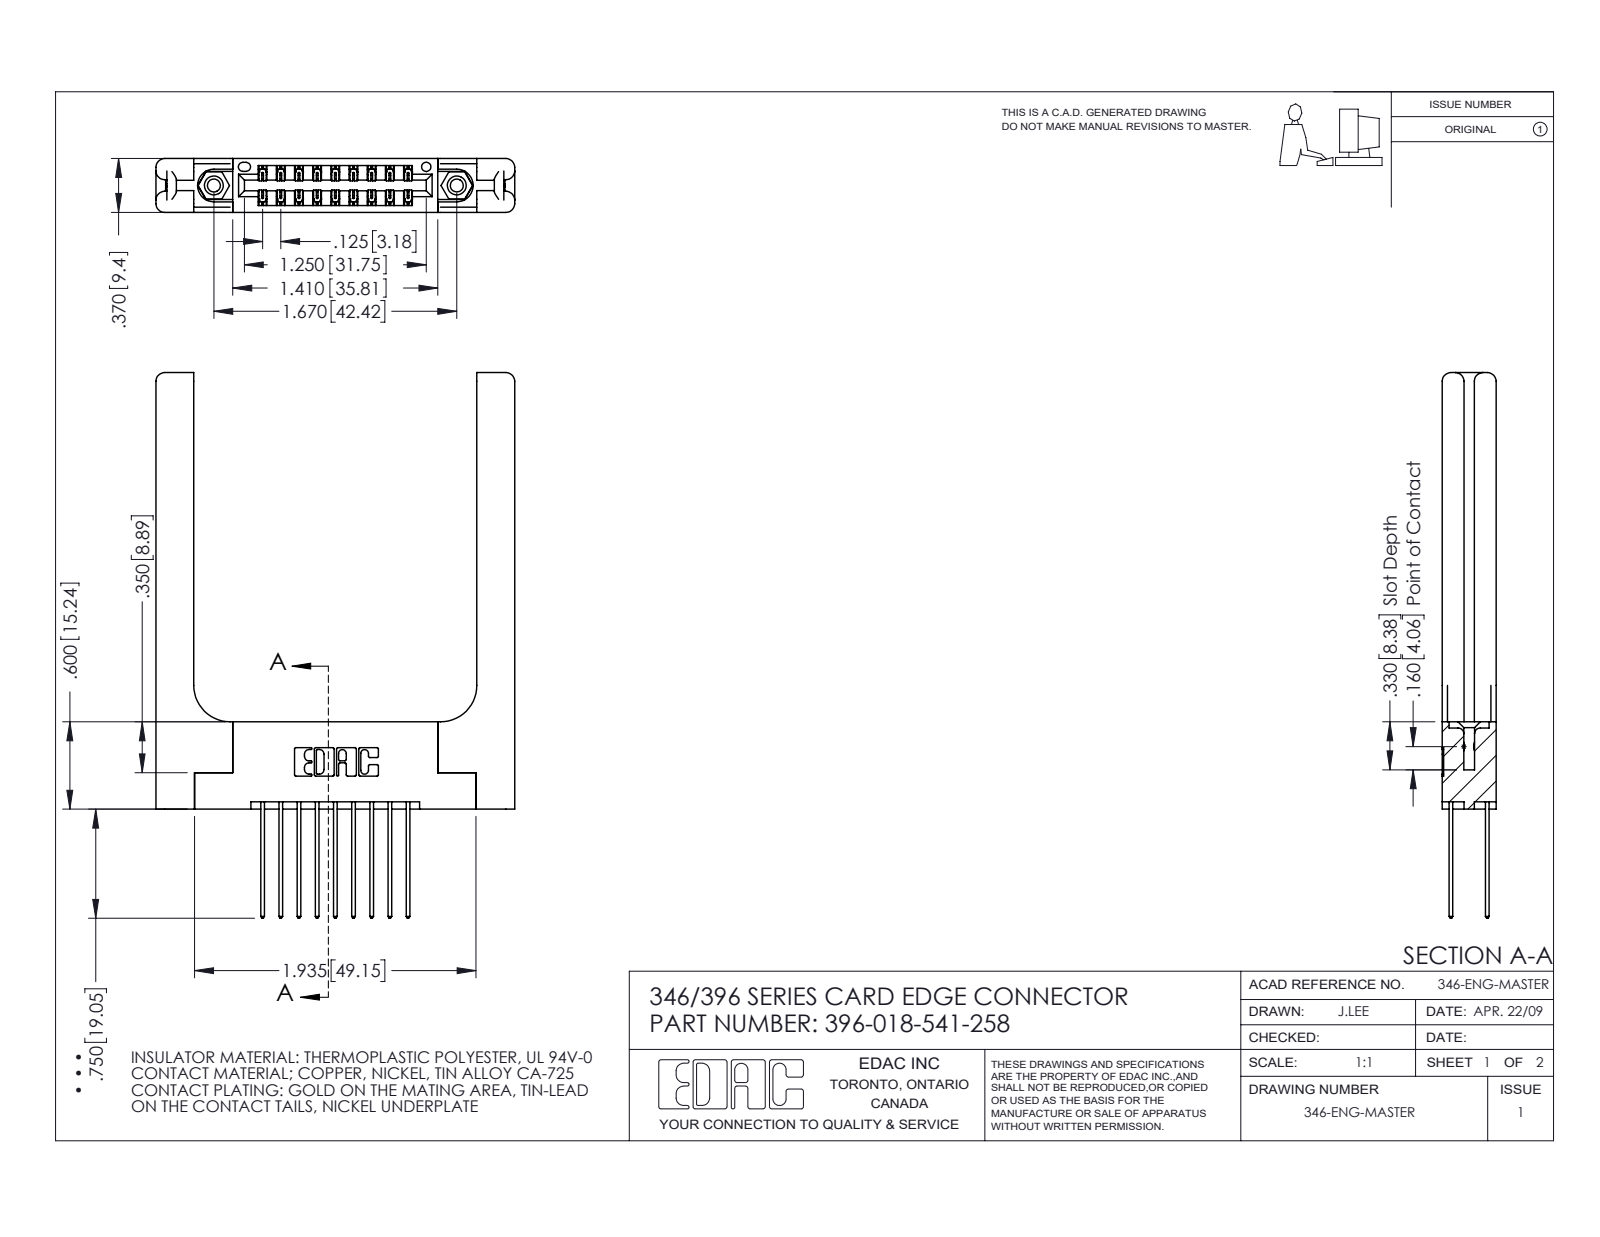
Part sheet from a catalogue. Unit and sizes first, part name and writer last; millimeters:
Units: millimetres
Overall size (bounding box): 95.3 × 62.6 × 9.4
Round holes (diameter × count): ⌀2.3 ×2, ⌀3.2 ×2, ⌀4 ×2, ⌀1.6 ×1
Round bosses / shafts (diameter × count): ⌀3.9 ×2
Partial cylindrical surfaces — rounded edges, fillets, slot ends (radius × count): R0.2 ×27, R0.3 ×22, R0.3 ×18, R1.5 ×16, R0.2 ×6, R0.8 ×6, R0.7 ×3, R0.4 ×2
Main face-to-face distances: 9.4, 3.8, 1.8, 3.8, 6.4, 1.2, 8.2, 2.6, 5.6, 4.4
Hole centre spacings: 6.2, 37.2, 42.4
Volume: 13 500 mm³ · Surface area: 13 140 mm²
Bodies: 23 solids, 1314 faces (854 planar, 400 cylindrical, 60 other)
Part name (STEP PRODUCT): 345-250-001_345-250-001-102; 396-018-541-258; 346-220-058_345-220-058; 345-292-001_345-293-141 (+1 more)
STEP written by: SolidWorks 2016 (CONFIG_CONTROL_DESIGN)
